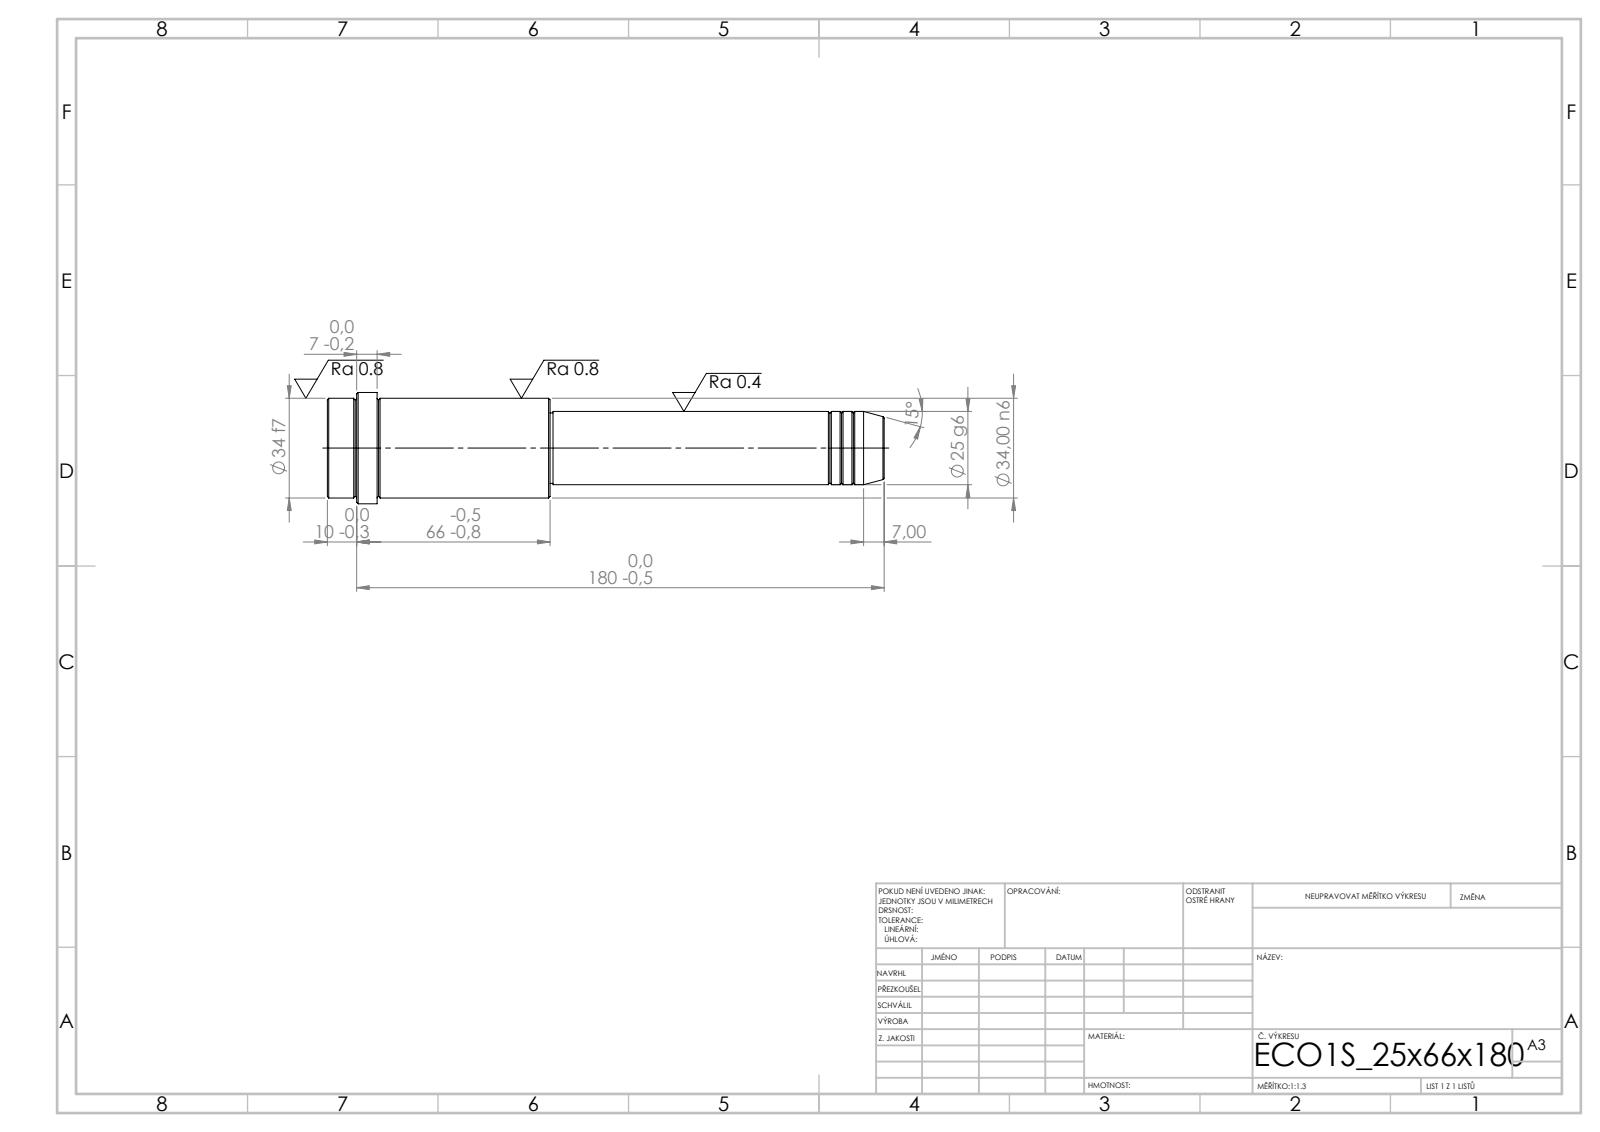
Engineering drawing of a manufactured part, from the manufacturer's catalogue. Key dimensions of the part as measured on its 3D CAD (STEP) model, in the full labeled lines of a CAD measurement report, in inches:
STEP written by: SolidWorks 2019 (CONFIG_CONTROL_DESIGN)
Units: inches
Bodies: 1 solid, 52 faces (6 planar, 16 cylindrical, 30 other)
Overall size (bounding box): 7.48 × 1.496 × 1.496
Volume: 7.677 in³ · Surface area: 30.19 in²
Round bosses / shafts (diameter × count): ⌀1.496 ×1, ⌀1.339 ×1, ⌀0.984 ×1, ⌀0.945 ×1
Main face-to-face distances: 2.992, 4.488, 7.48, 6.811, 2.323, 0.669, 7.087, 2.598, 0.276, 0.394
